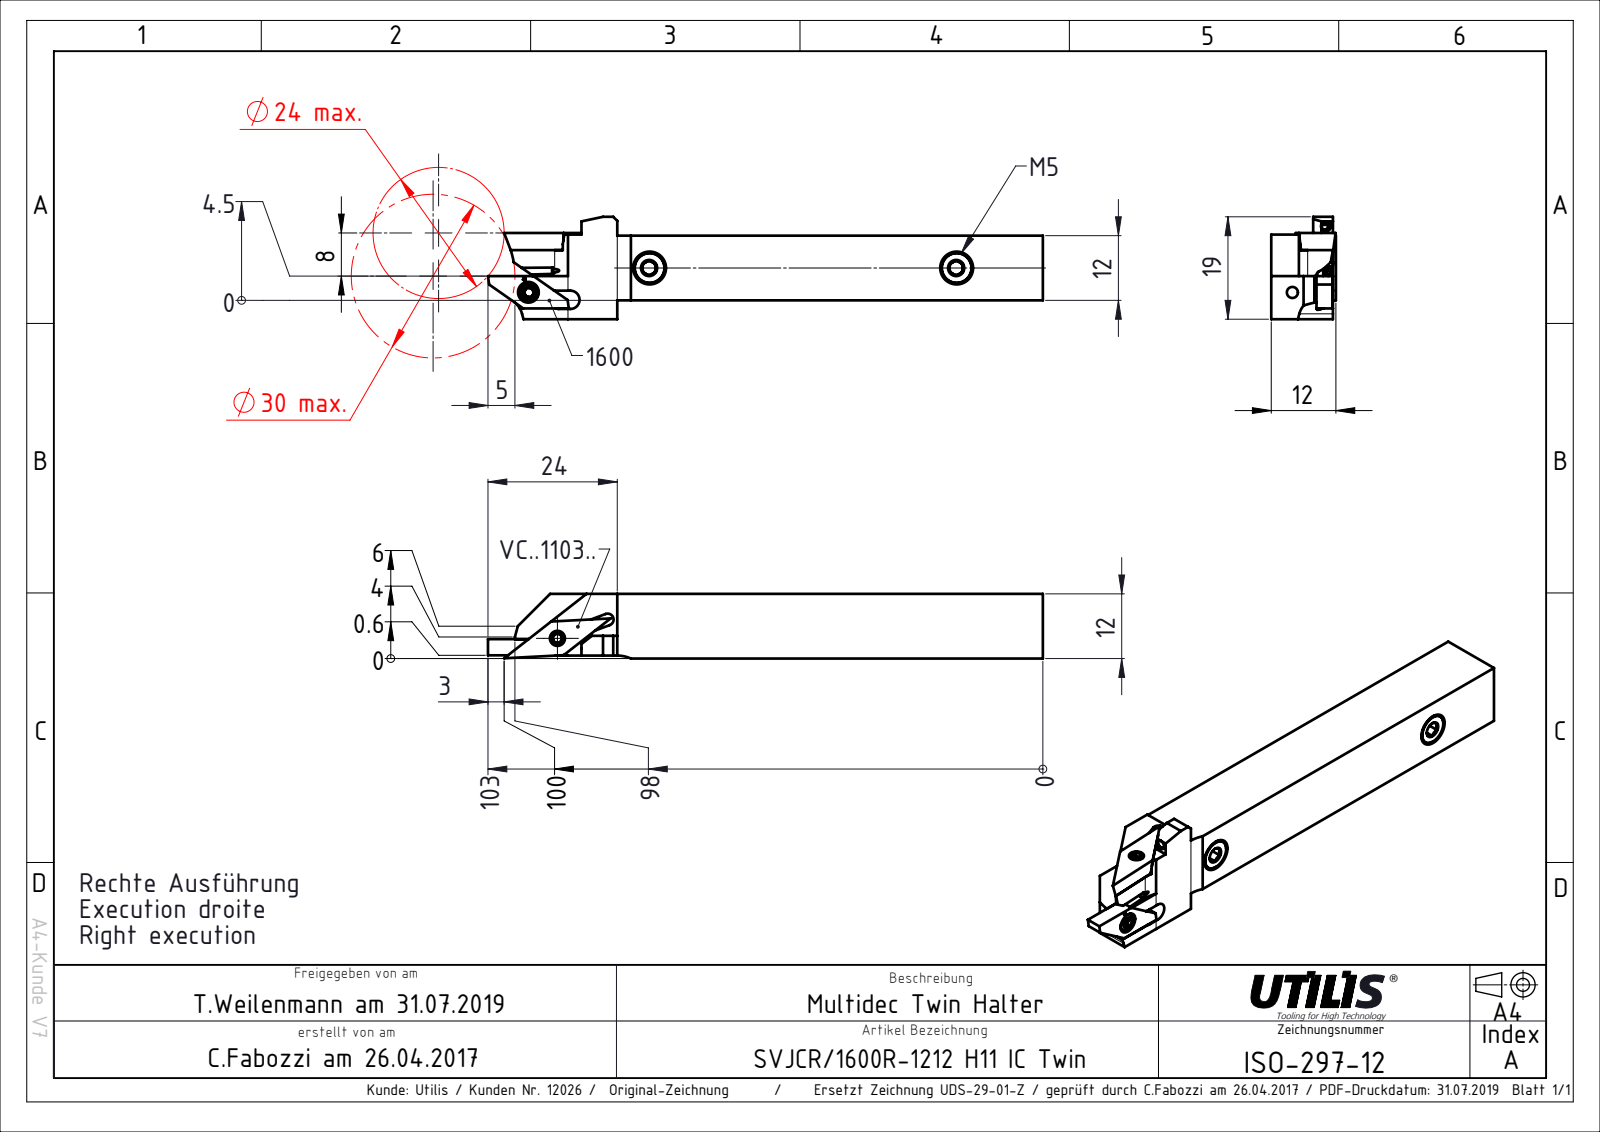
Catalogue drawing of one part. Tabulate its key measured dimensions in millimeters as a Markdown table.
| quantity | value |
| --- | --- |
| part name | ISO-297-12 |
| STEP written by | SolidWorks 2016 (AUTOMOTIVE_DESIGN) |
| units | millimeters |
| bodies | 1 solid, 88 faces (72 planar, 14 cylindrical, 2 other) |
| overall size | 103 × 19 × 12 |
| volume | 14 182 mm³ |
| surface area | 5 422 mm² |
| round holes (diameter × count) | 1.8 × 1 |
| partial cylindrical surfaces (radius × count) | 6.1 × 3, 0.25 × 2, 0.5 × 1, 1.1 × 1, 1.55 × 1, 1.7 × 1, 4.1 × 1, 15.19 × 1 |
| main face-to-face distances | 12, 3.5, 15.5, 8, 0.5, 4.5, 7.5, 16, 12.5, 11.5 |
